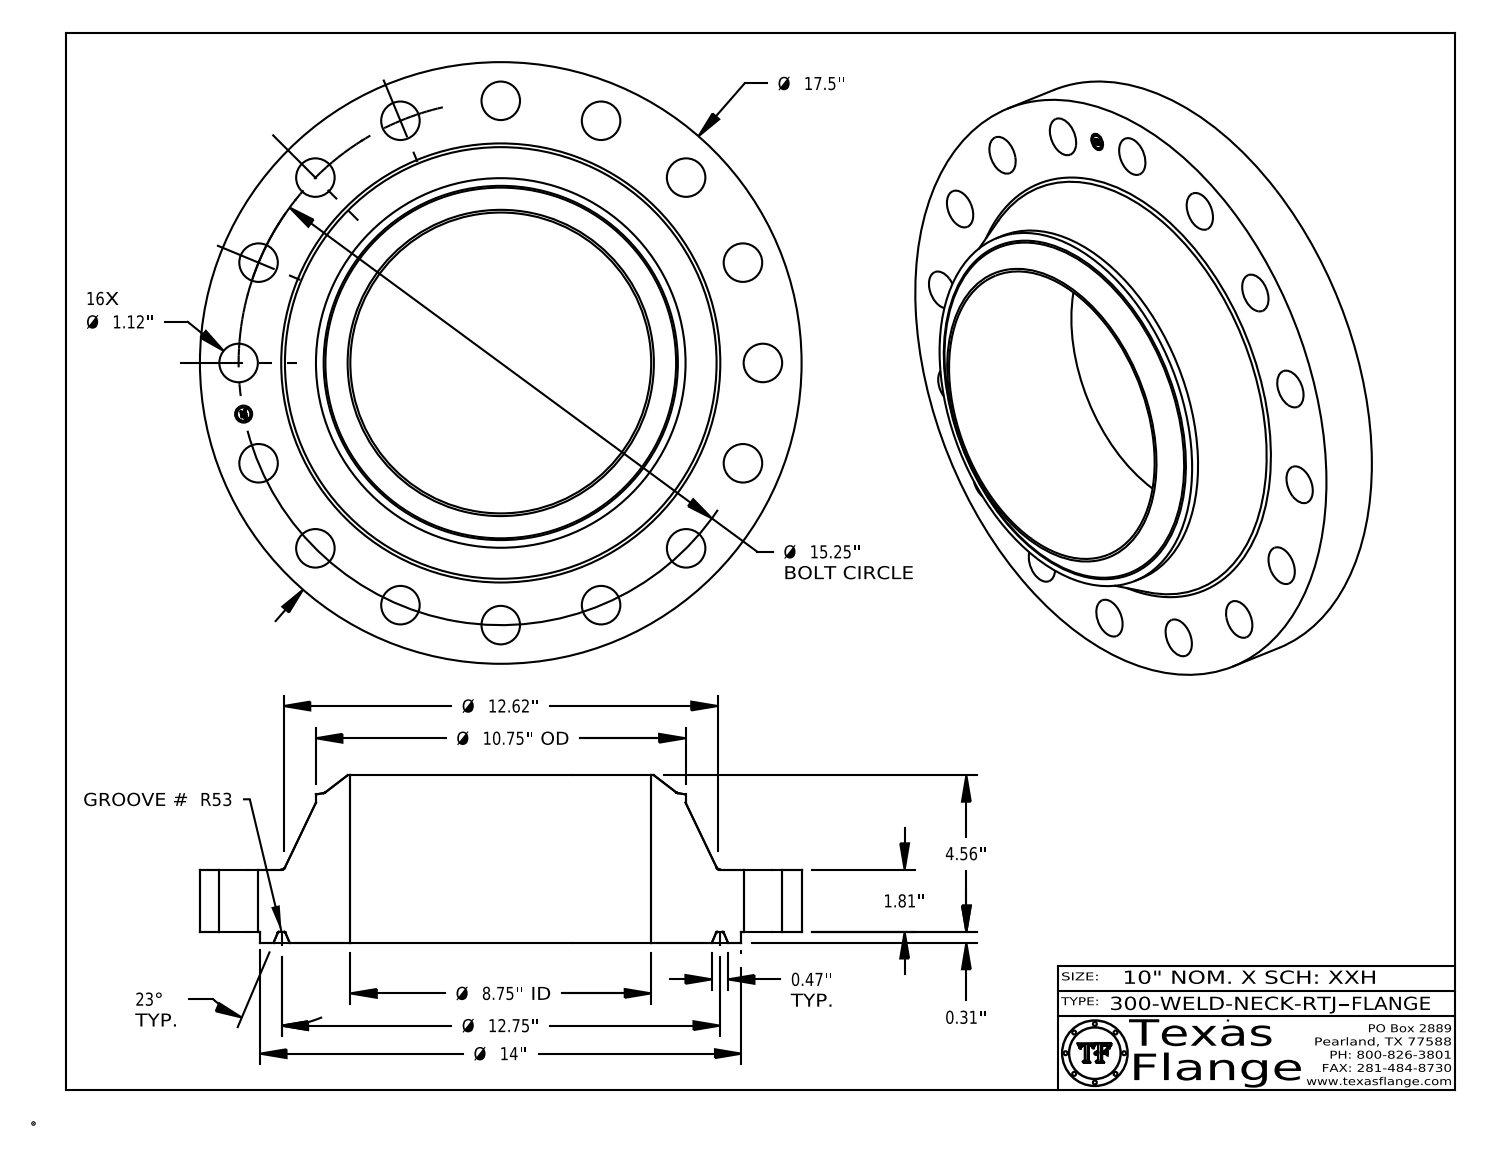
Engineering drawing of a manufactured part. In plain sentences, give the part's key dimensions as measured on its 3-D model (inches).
The part is named "300-WELD-NECK-RTJ". Its 3-D file was written by "CATIA V5 STEP AP214 (AUTOMOTIVE_DESIGN)". It is 1 solid with 449 faces: 371 planar, 60 cylindrical and 18 other. Overall it measures 17.5 by 17.5 by 4.873 inches. Its volume is 430.3 cubic inches and its surface area 752.6 square inches. Round holes: 16 of diameter 1.12, 1 of diameter 0.495, 1 of diameter 8.75. Round bosses or shafts: 8 of diameter 0.03, 1 of diameter 17.5, 1 of diameter 14, 1 of diameter 10.75, 1 of diameter 0.39. The main face-to-face distances are 1.81, 0.313, 2.123, 4.873, 4.56, 2.75, 0.015, 2.108, 1.795, 2.765. The hole center spacings are 8.472, 10.783, 14.957, 14.089, 7.625, 2.975, 2.975, 5.836.
